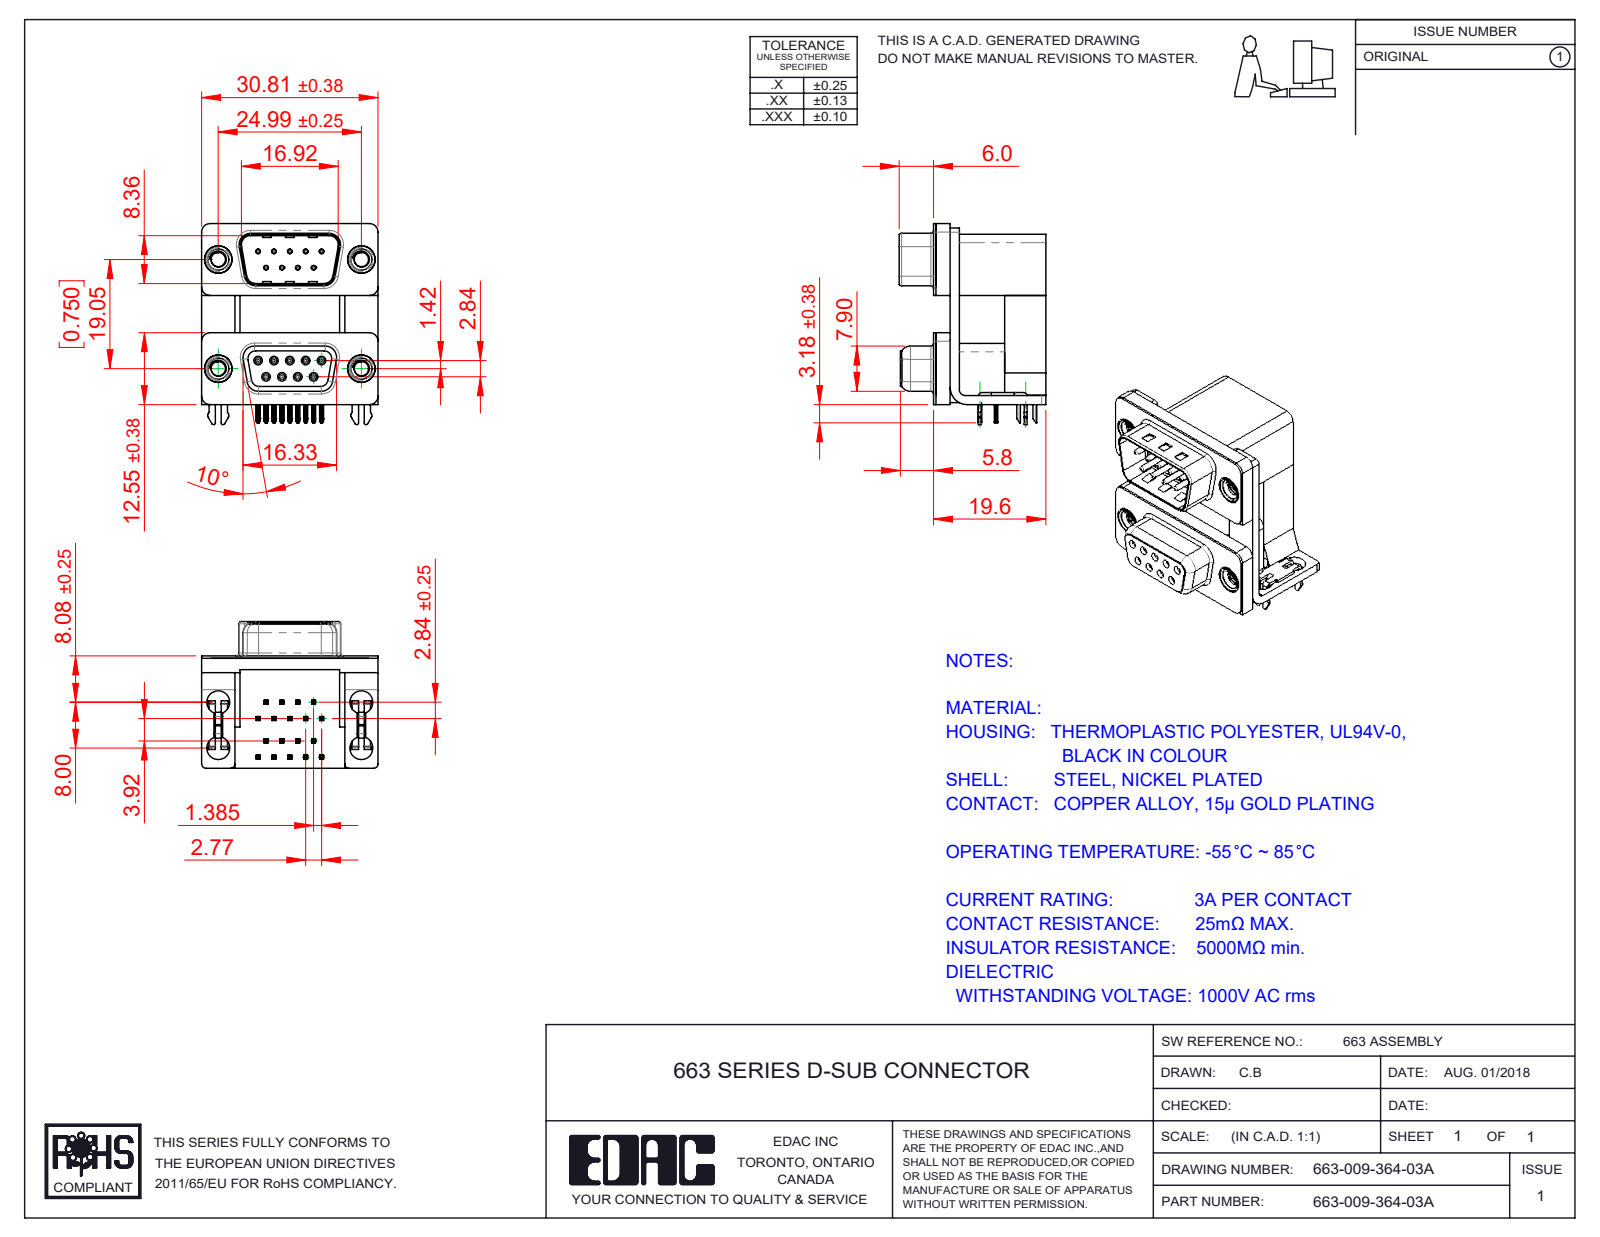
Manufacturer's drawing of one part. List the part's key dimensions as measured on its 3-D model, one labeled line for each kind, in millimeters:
Part name (STEP PRODUCT): 663 Threaded Rivet_M3; 663 2 Prong Board Lock_3; 663 Housing Upper_09 Contacts M; 663 Housing Lower_09 Contacts (+8 more)
STEP written by: SolidWorks 2020 (CONFIG_CONTROL_DESIGN)
Units: millimetres
Bodies: 31 solids, 2685 faces (1365 planar, 753 cylindrical, 567 other)
Overall size (bounding box): 35.1 × 30.81 × 25.6
Volume: 10 810 mm³ · Surface area: 12 747 mm²
Round holes (diameter × count): ⌀0.8 ×18, ⌀0.35 ×9, ⌀0.9 ×9, ⌀4 ×8, ⌀2.5 ×4, ⌀3.5 ×4, ⌀4.8 ×4, ⌀5 ×4
Round bosses / shafts (diameter × count): ⌀1.2 ×9, ⌀0.75 ×9, ⌀4.9 ×4, ⌀4.75 ×4, ⌀3.9 ×4
Partial cylindrical surfaces — rounded edges, fillets, slot ends (radius × count): R0.1 ×74, R0.25 ×46, R0.15 ×36, R0.12 ×18, R0.35 ×18, R0.5 ×16, R1.5 ×15, R0.75 ×10
Main face-to-face distances: 0.4, 2.5, 16.7, 19.2, 9.5, 7.2, 12, 1.6, 19.6, 12.4
Hole centre spacings: 3.16, 2.77, 19.25, 19.05, 5.54, 19.84, 16.27, 21.93
